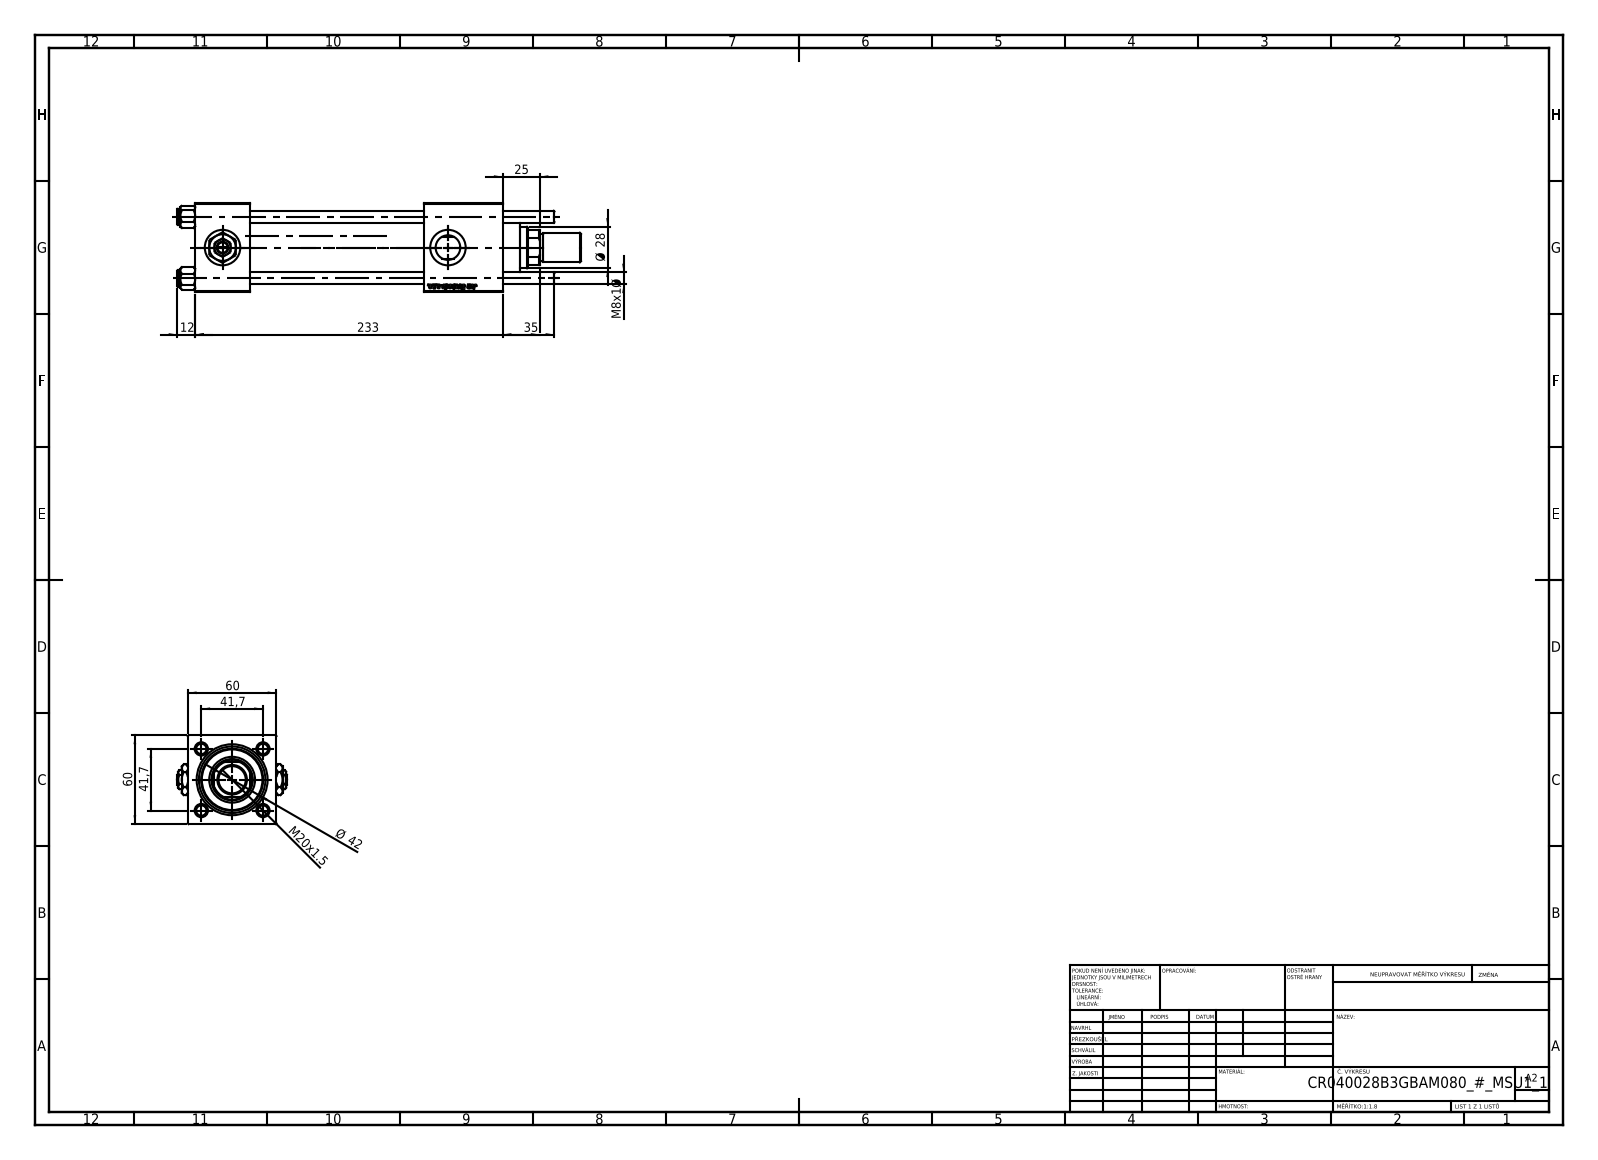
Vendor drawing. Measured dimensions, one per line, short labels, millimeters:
name: V215CR_B_TYCINKA; V215CR_B-1; V215_VC_A; ROD_END_AH (+3 more)
written by: SolidWorks 2019 (CONFIG_CONTROL_DESIGN)
unit: mm
bodies: 14 solids, 1273 faces (485 planar, 92 cylindrical, 696 other)
size: 273 × 74 × 60
volume: 514 305 mm³; area: 152 729 mm²
holes: 4× ⌀8, 2× ⌀7, 2× ⌀16.66, 2× ⌀24, 1× ⌀18.5, 1× ⌀28, 1× ⌀31, 1× ⌀40, 1× ⌀45
bosses: 4× ⌀11, 1× ⌀46, 1× ⌀42, 1× ⌀20, 1× ⌀18
rounds: 1× R13.5
face distances: 60, 37, 155, 118, 53, 179.3, 142.3, 24.3, 208, 171
hole spacings: 29.49, 41.7, 58.97, 152.5
